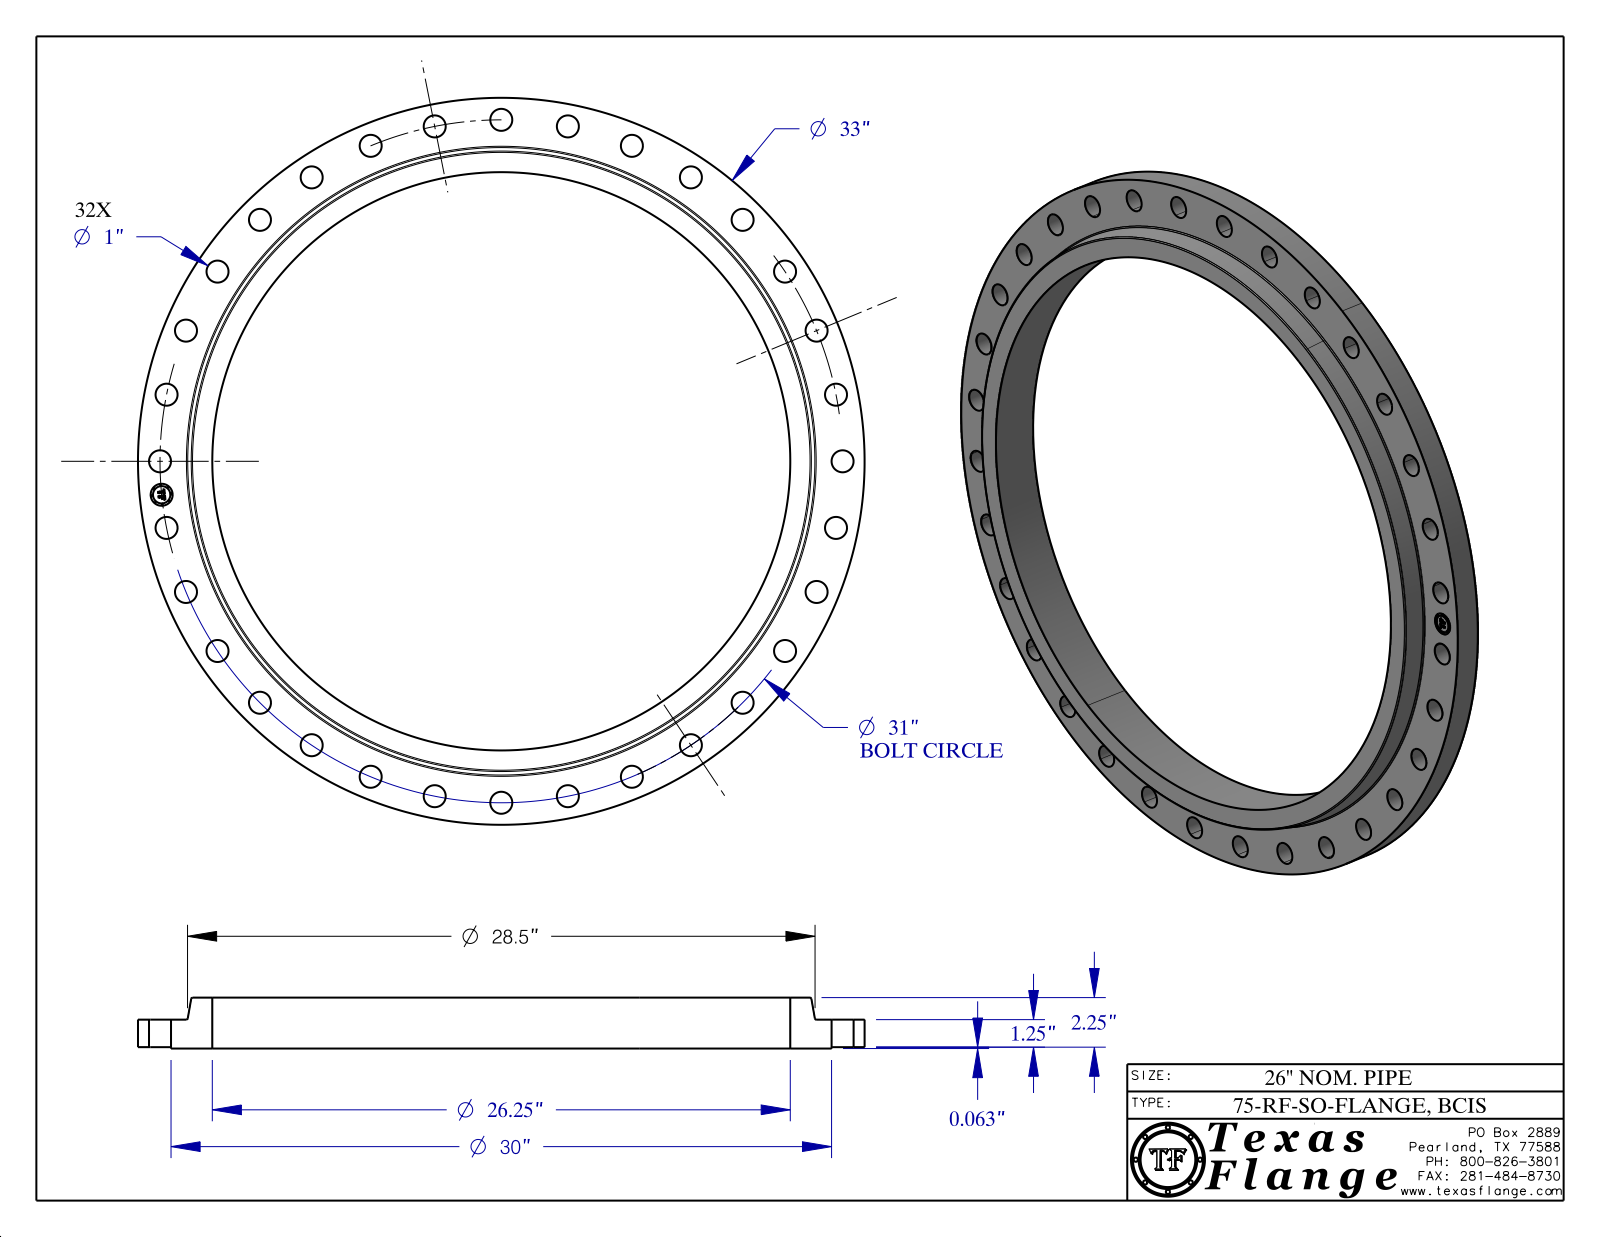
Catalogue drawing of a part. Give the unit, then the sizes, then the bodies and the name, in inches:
Units: inches
Overall size (bounding box): 33 × 33 × 2.313
Round holes (diameter × count): ⌀1 ×33, ⌀26.25 ×1
Round bosses / shafts (diameter × count): ⌀0.061 ×8, ⌀33 ×1, ⌀30 ×1, ⌀0.788 ×1
Main face-to-face distances: 1.313, 0.063, 1.25, 2.313, 2.25, 1, 0.015, 1.298, 1.235, 1.015
Hole centre spacings: 3.039, 8.999, 14.613, 23.963, 30.851, 21.92, 25.776, 28.641
Volume: 460.5 in³ · Surface area: 1 102 in²
Bodies: 1 solid, 465 faces (369 planar, 90 cylindrical, 6 other)
Part name (STEP PRODUCT): 75-RF-SO
STEP written by: CATIA V5 STEP AP214 (AUTOMOTIVE_DESIGN)
